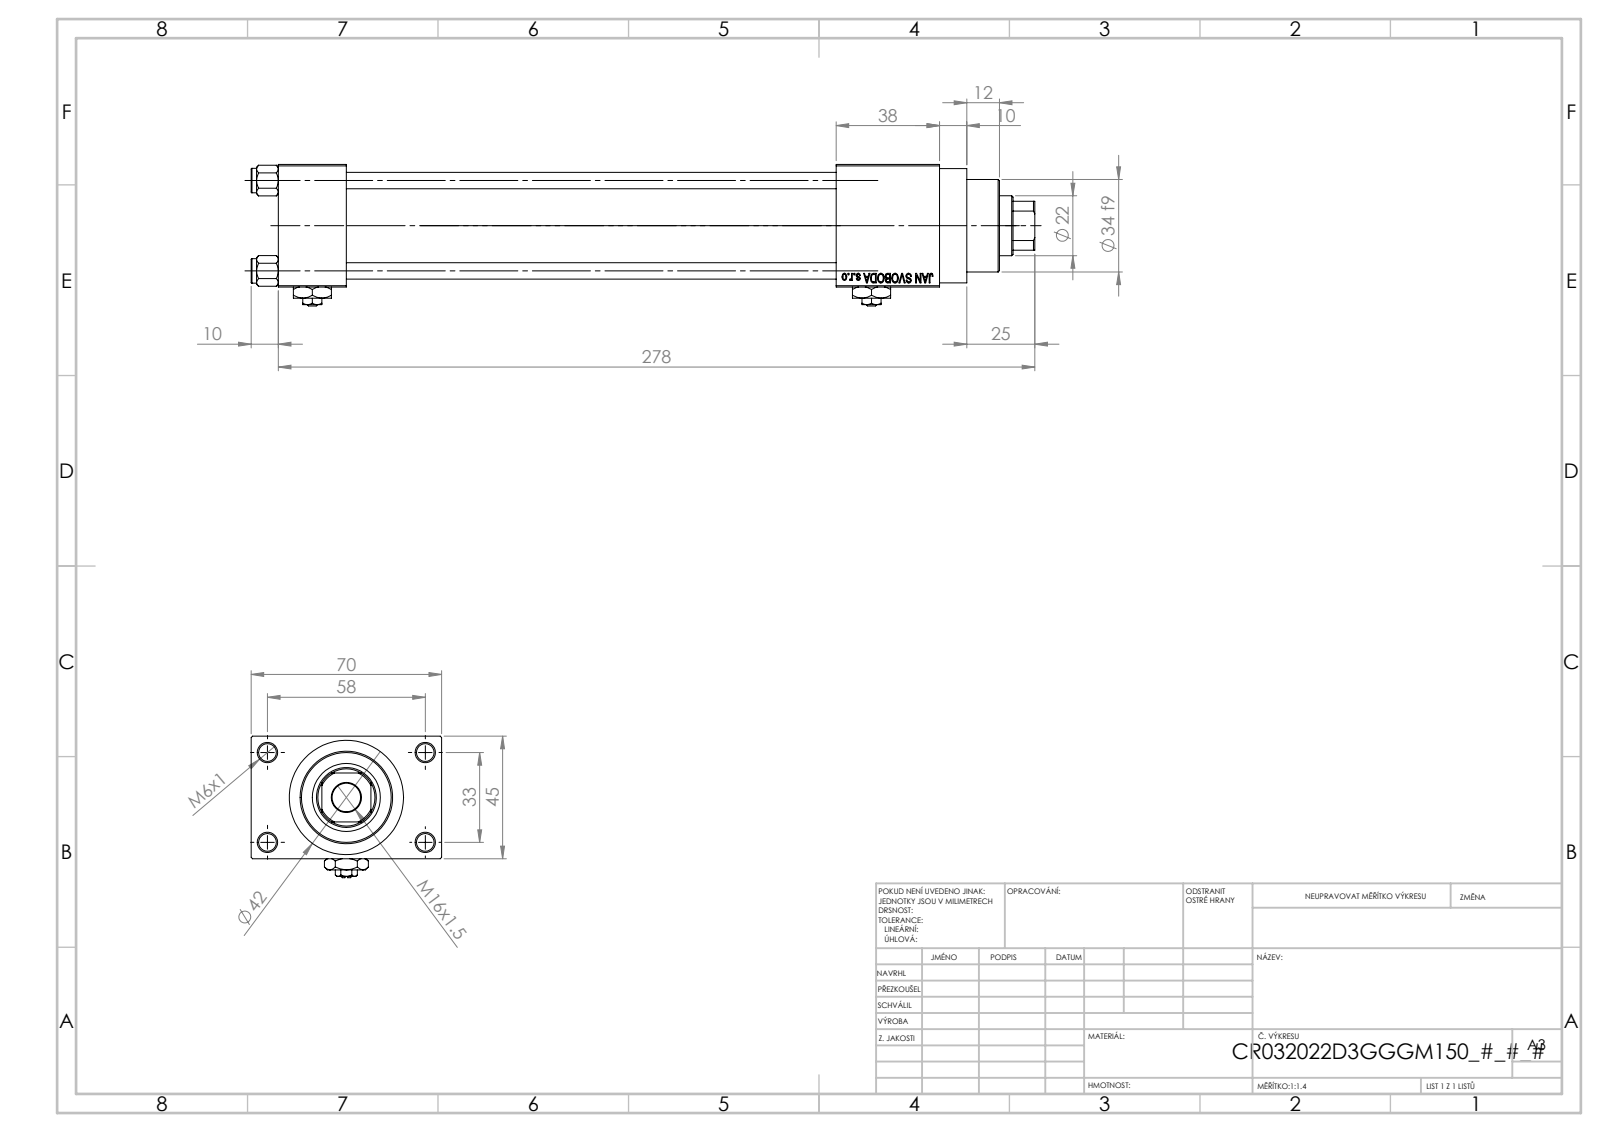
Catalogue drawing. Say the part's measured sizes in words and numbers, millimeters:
The part is named "V215CR_D_Body; Zatka_pro_OIL_PORT; V215CR_D_TYCINKA; V215_VC_A (+2 more)". Its 3-D file was written by "SolidWorks 2019 (CONFIG_CONTROL_DESIGN)". It is 13 solids with 1202 faces: 542 planar, 100 cylindrical and 560 other. Overall it measures 288 by 70 by 52 millimeters. Its volume is 350 370 cubic millimeters and its surface area 128 575 square millimeters. Round holes: 4 of diameter 6, 4 of diameter 6.5, 2 of diameter 7, 2 of diameter 13.16, 2 of diameter 20, 1 of diameter 10.5, 1 of diameter 22, 1 of diameter 24, 1 of diameter 25, 1 of diameter 32, 1 of diameter 33. Round bosses or shafts: 4 of diameter 9, 1 of diameter 42, 1 of diameter 38, 1 of diameter 34. Partial cylindrical surfaces (rounded edges, fillets, slot ends): 1 of radius 10.5. The main face-to-face distances are 45, 25, 12.5, 57.5, 180, 205, 218, 38, 70, 243. The hole center spacings are 12.4, 23.48, 33.2, 33.37, 35.35, 45.6, 56.35, 33.
